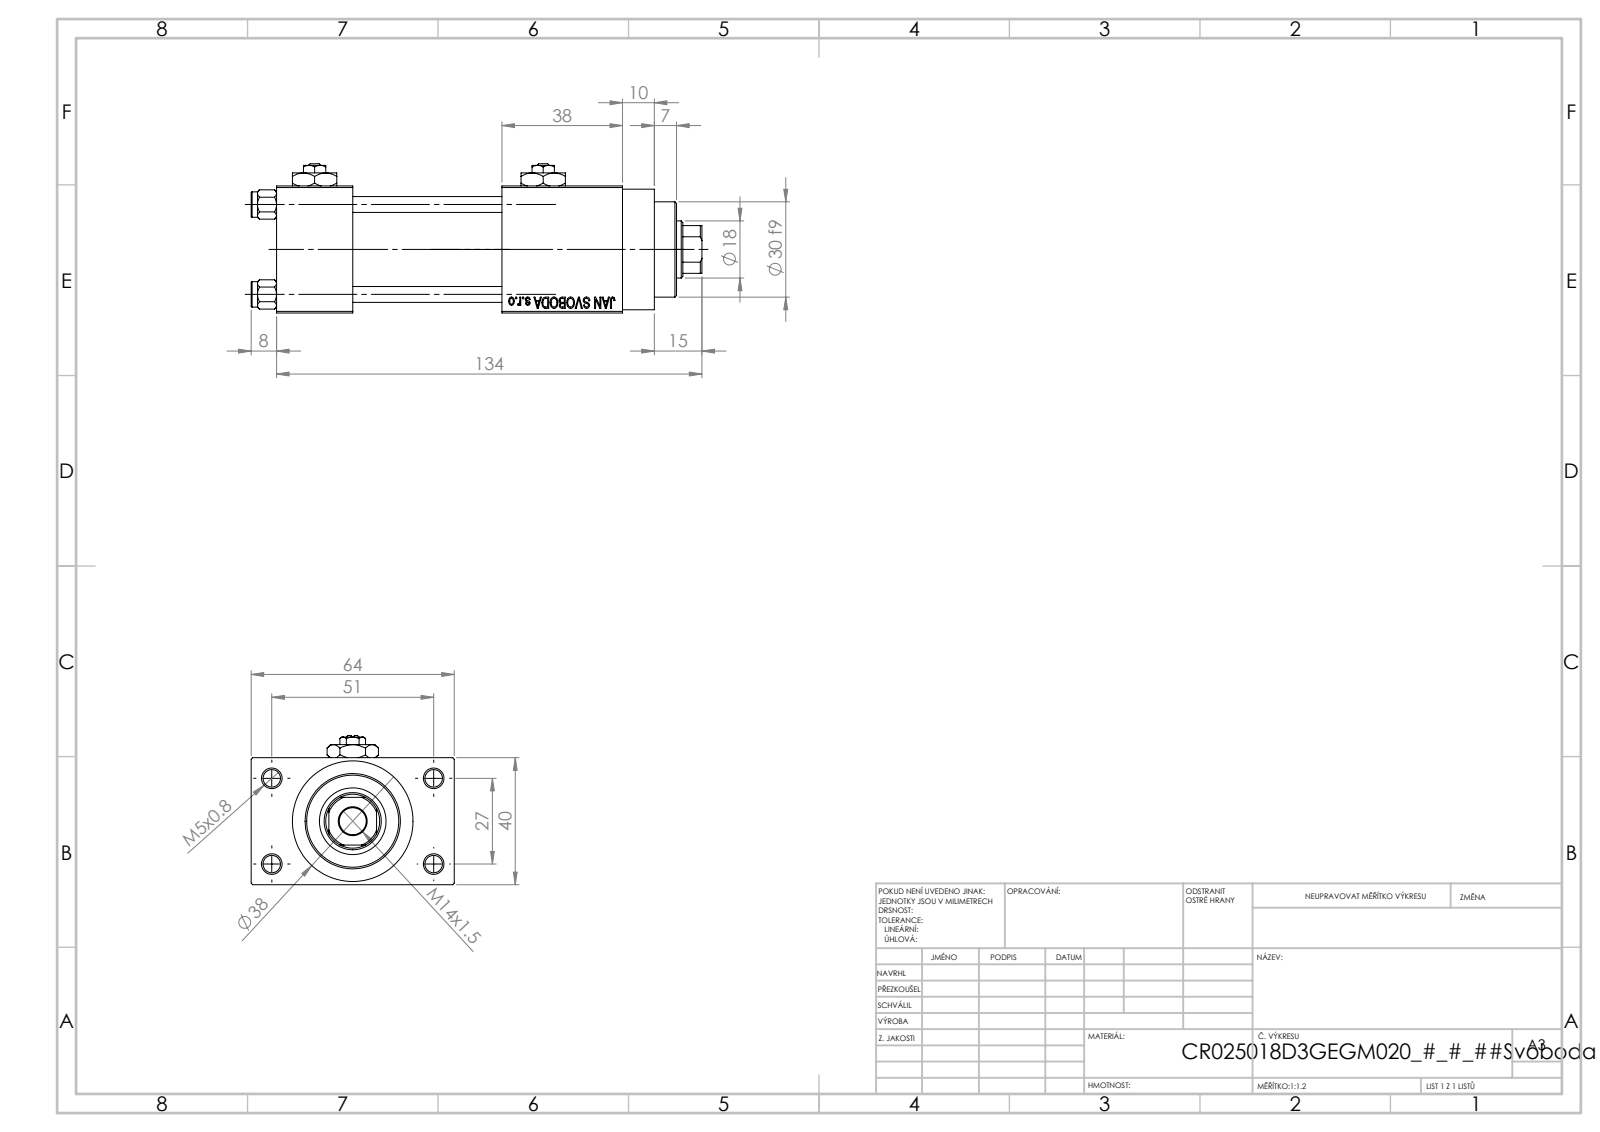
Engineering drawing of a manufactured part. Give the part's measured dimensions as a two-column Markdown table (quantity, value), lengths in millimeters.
| quantity | value |
| --- | --- |
| part name | V215CR_VCP_D; Zatka_pro_OIL_PORT; V215_VC_A; V215CR_D_TYCINKA (+2 more) |
| STEP written by | SolidWorks 2019 (CONFIG_CONTROL_DESIGN) |
| units | millimeters |
| bodies | 13 solids, 1199 faces (541 planar, 98 cylindrical, 560 other) |
| overall size | 142 × 64 × 47 |
| volume | 179 762 mm³ |
| surface area | 65 864 mm² |
| round holes (diameter × count) | 5 × 4, 5.5 × 4, 20 × 3, 7 × 2, 13.16 × 2, 8.5 × 1, 18 × 1, 21 × 1, 25 × 1, 30 × 1 |
| round bosses / shafts (diameter × count) | 8 × 4, 38 × 1, 31 × 1 |
| partial cylindrical surfaces (radius × count) | 8.5 × 1 |
| main face-to-face distances | 40, 52, 12, 47, 24, 71, 64, 38, 85, 109 |
| hole center spacings | 11.37, 20.01, 28.3, 28.85, 29.89, 39.66, 48.34, 27 |
